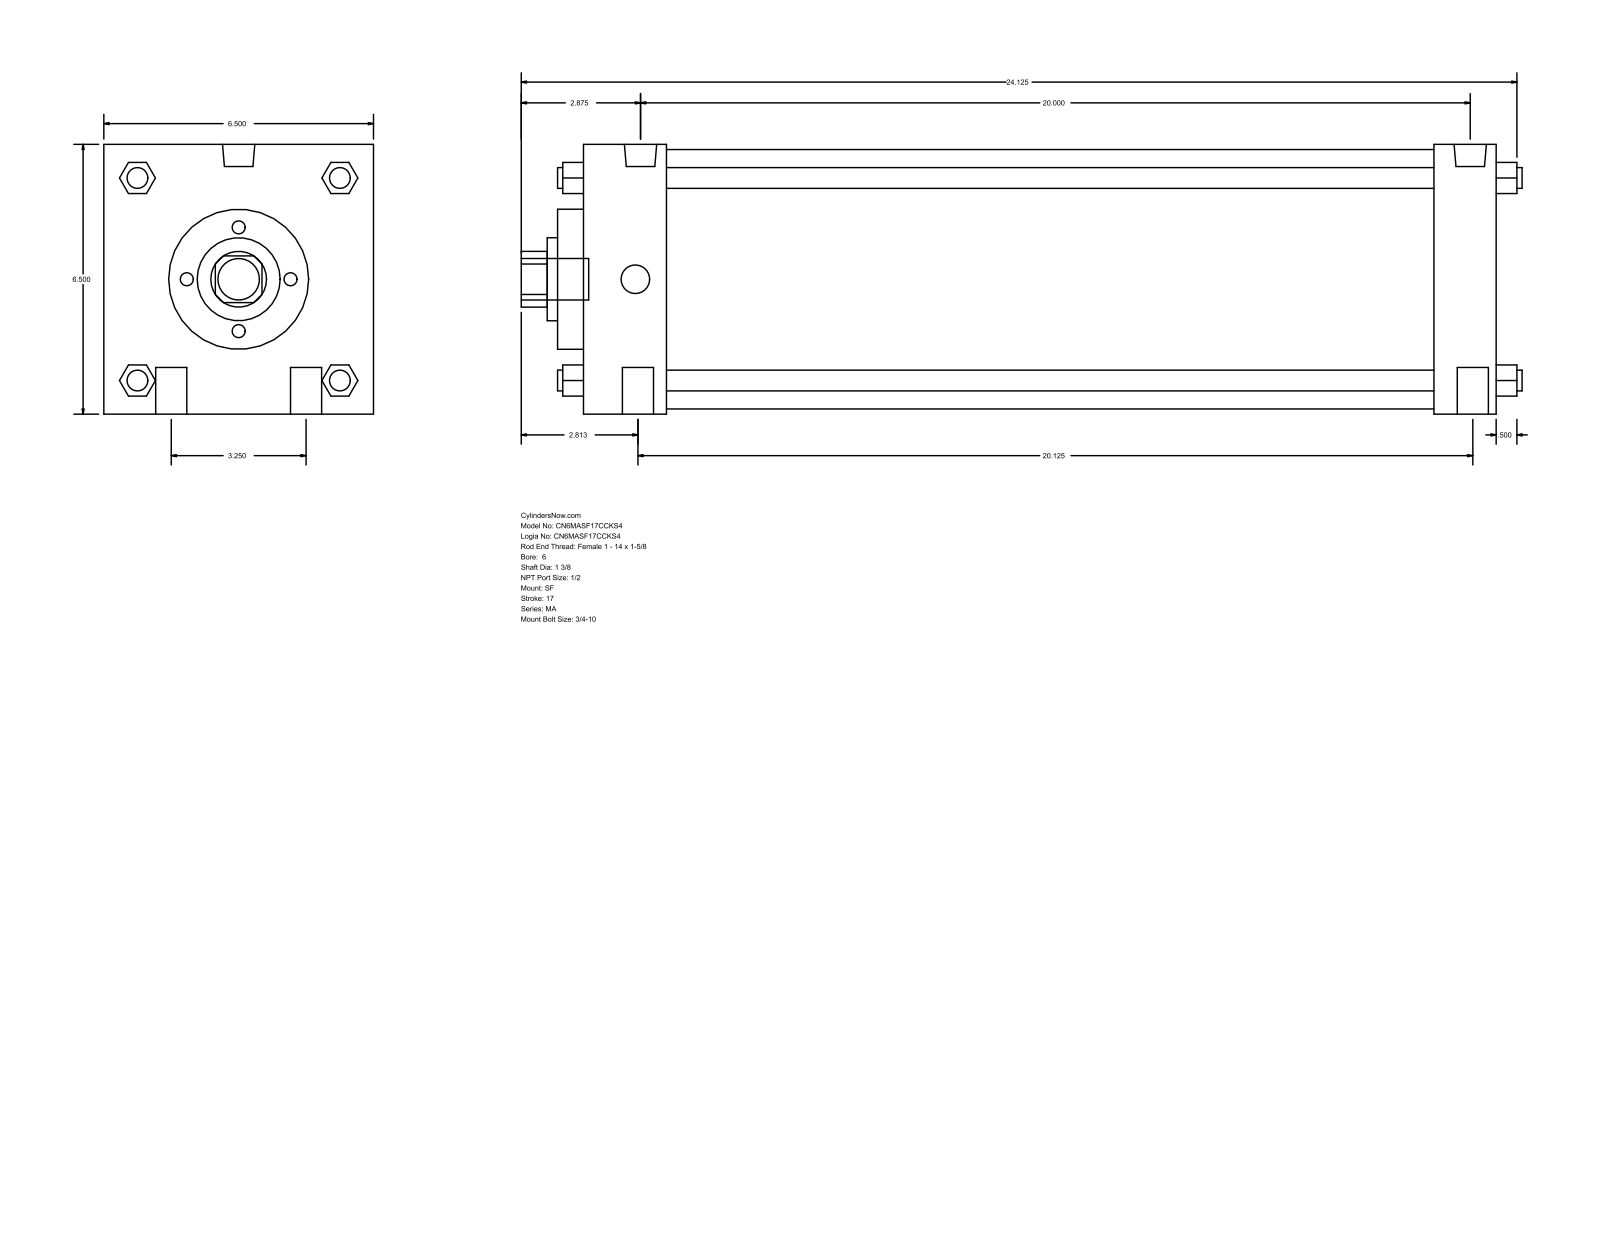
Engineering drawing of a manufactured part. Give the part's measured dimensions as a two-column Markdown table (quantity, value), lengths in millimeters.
| quantity | value |
| --- | --- |
| part name | MA_SF__0600_1.375 |
| STEP written by | GSSL Pune (CONFIG_CONTROL_DESIGN) |
| units | millimeters |
| bodies | 0 solids, 126 faces (95 planar, 31 cylindrical, 0 other) |
| overall size | 612.77 × 165.1 × 165.1 |
| round holes (diameter × count) | 34.92 × 1, 50.8 × 1, 85.72 × 1, 158.75 × 1 |
| round bosses / shafts (diameter × count) | 19.05 × 4, 12.7 × 4, 19.77 × 2, 17.46 × 2, 25.4 × 1 |
| partial cylindrical surfaces (radius × count) | 17.06 × 1 |
| main face-to-face distances | 165.1, 558.8, 520.7, 50.8, 38.1, 469.9, 508, 15.87, 574.67, 66.67 |
